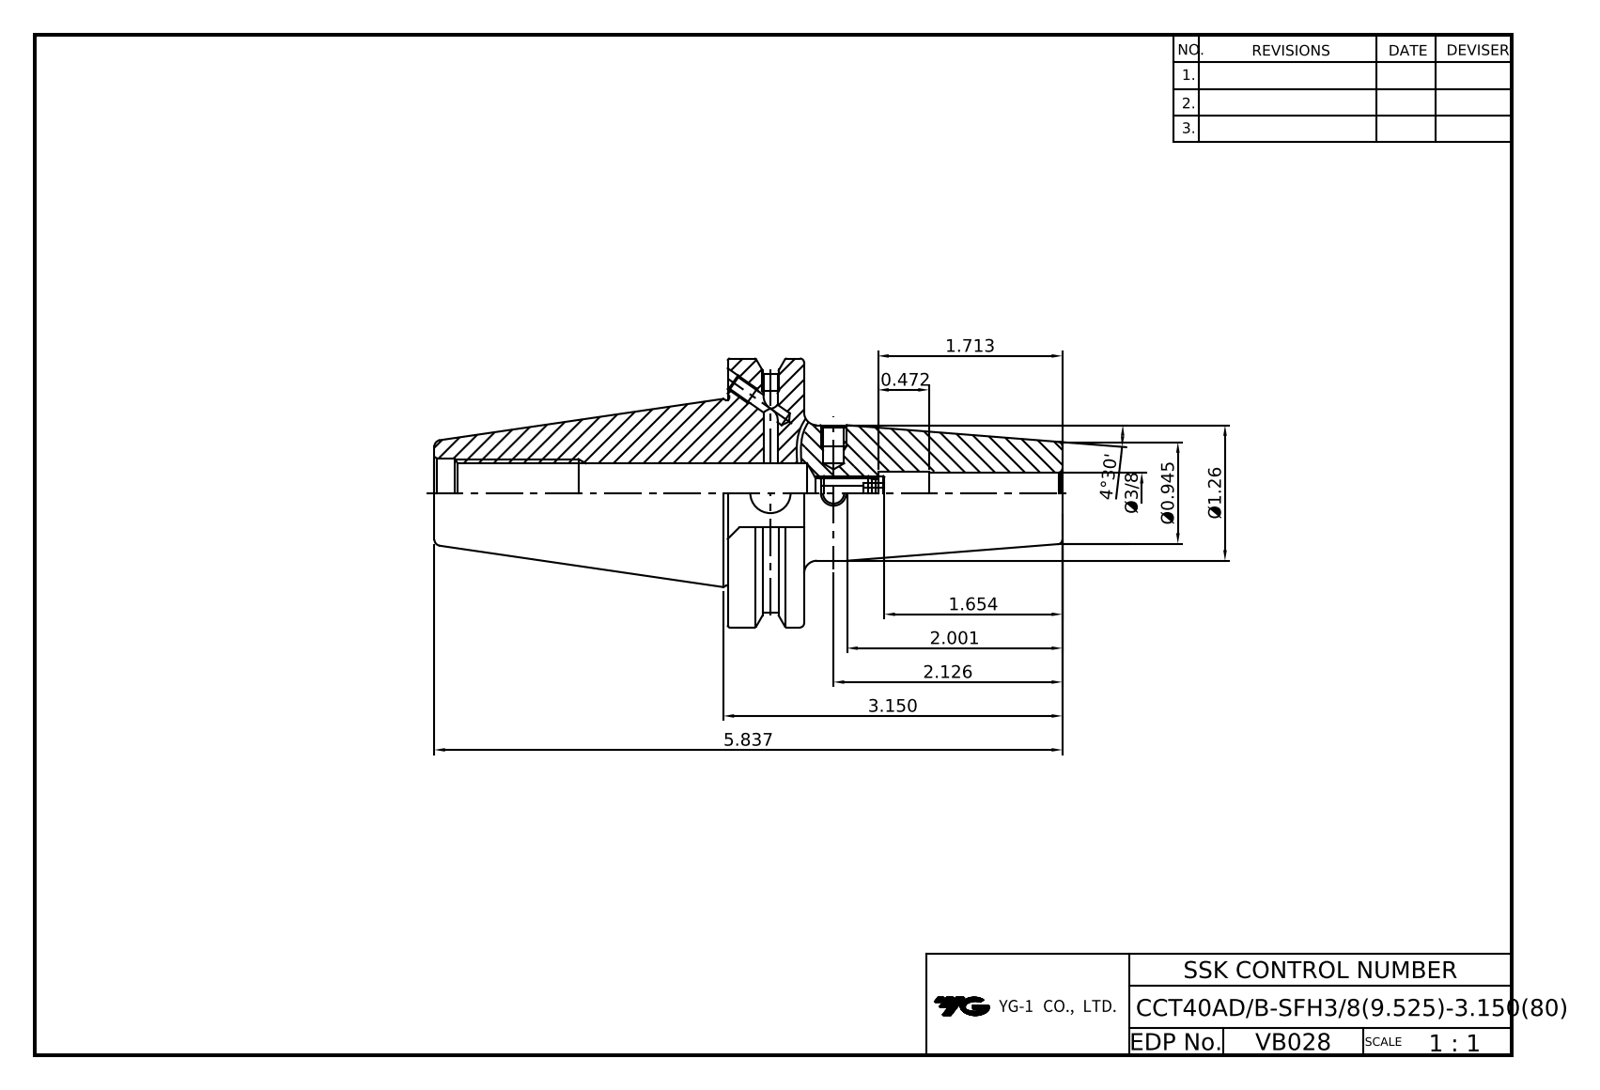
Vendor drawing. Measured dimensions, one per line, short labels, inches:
name: VB028-CCT40ADB-SFH0_375-3_15
written by: PRO/ENGINEER BY PARAMETRIC TECHNOLOGY CORPORATION, 2012130 (CONFIG_CONTROL_DESIGN)
unit: in
bodies: 1 solid, 161 faces (33 planar, 66 cylindrical, 62 other)
size: 5.837 × 2.5 × 2.416
volume: 8.452 in³; area: 45.61 in²
holes: 3× ⌀0.13, 3× ⌀0.138, 3× ⌀0.157, 2× ⌀0.197, 2× ⌀0.375, 1× ⌀0.165, 1× ⌀0.28, 1× ⌀0.399, 1× ⌀0.551, 1× ⌀0.642
bosses: 1× ⌀2.5, 1× ⌀1.26
rounds: 1× R1.11
face distances: 0.711, 3.111, 2.4, 1.898, 0.644, 2.726, 3.437, 5.837, 3.201, 0.475
hole spacings: 0.587
